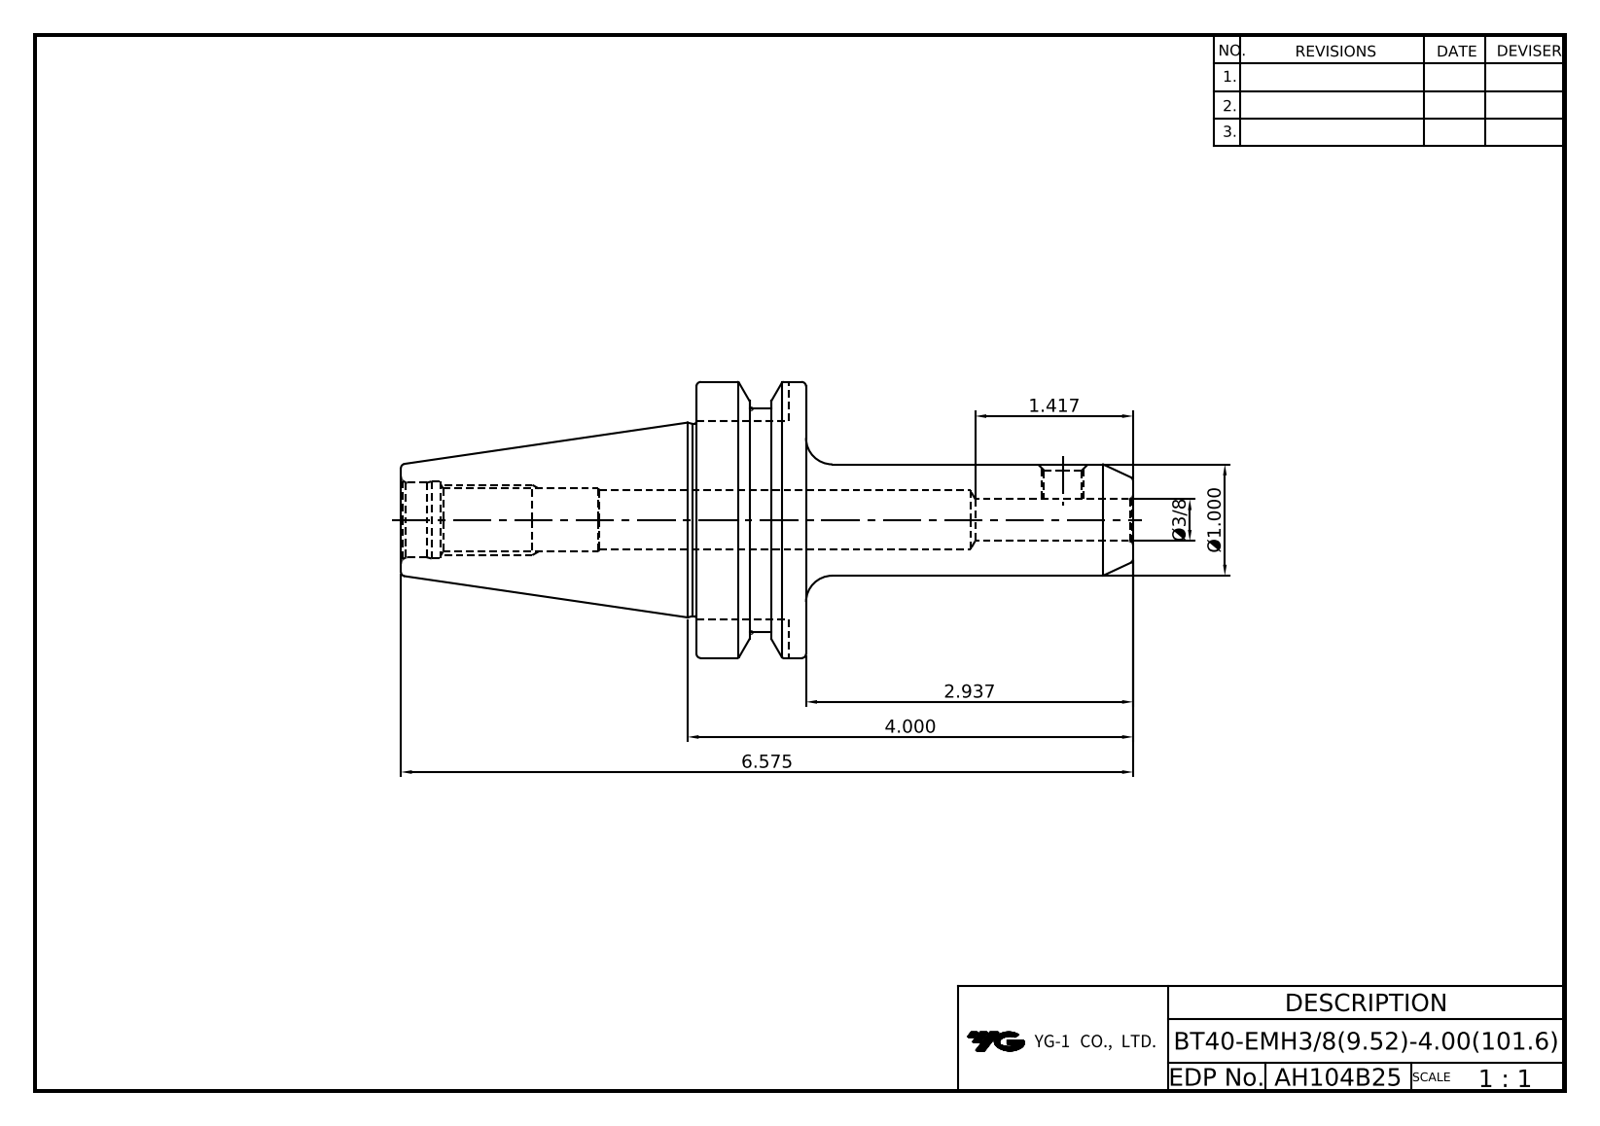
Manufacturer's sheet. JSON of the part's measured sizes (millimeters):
{"part_name": "LO-BT40-EMH9.525-101.6", "step_written_by": "Autodesk Inventor 2022 (AUTOMOTIVE_DESIGN)", "units": "millimeters", "bodies": {"solids": 1, "faces": 52, "planar": 15, "cylindrical": 15, "other": 22}, "overall_size": [167, 63, 63], "volume_mm3": 148940, "surface_area_mm2": 30844, "round_holes": [[8.38, 1], [9.53, 1], [13.5, 1], [13.84, 1], [17, 1], [17.6, 1]], "round_bosses_or_shafts": [[63, 1], [52.6, 1], [44, 1], [25.4, 1]], "partial_cylinders_radius": [[8.05, 1]], "face_to_face_distances": [25, 45.2, 16.1, 67.4, 92.4, 167, 99.6, 74.6, 84.5, 17.1]}
